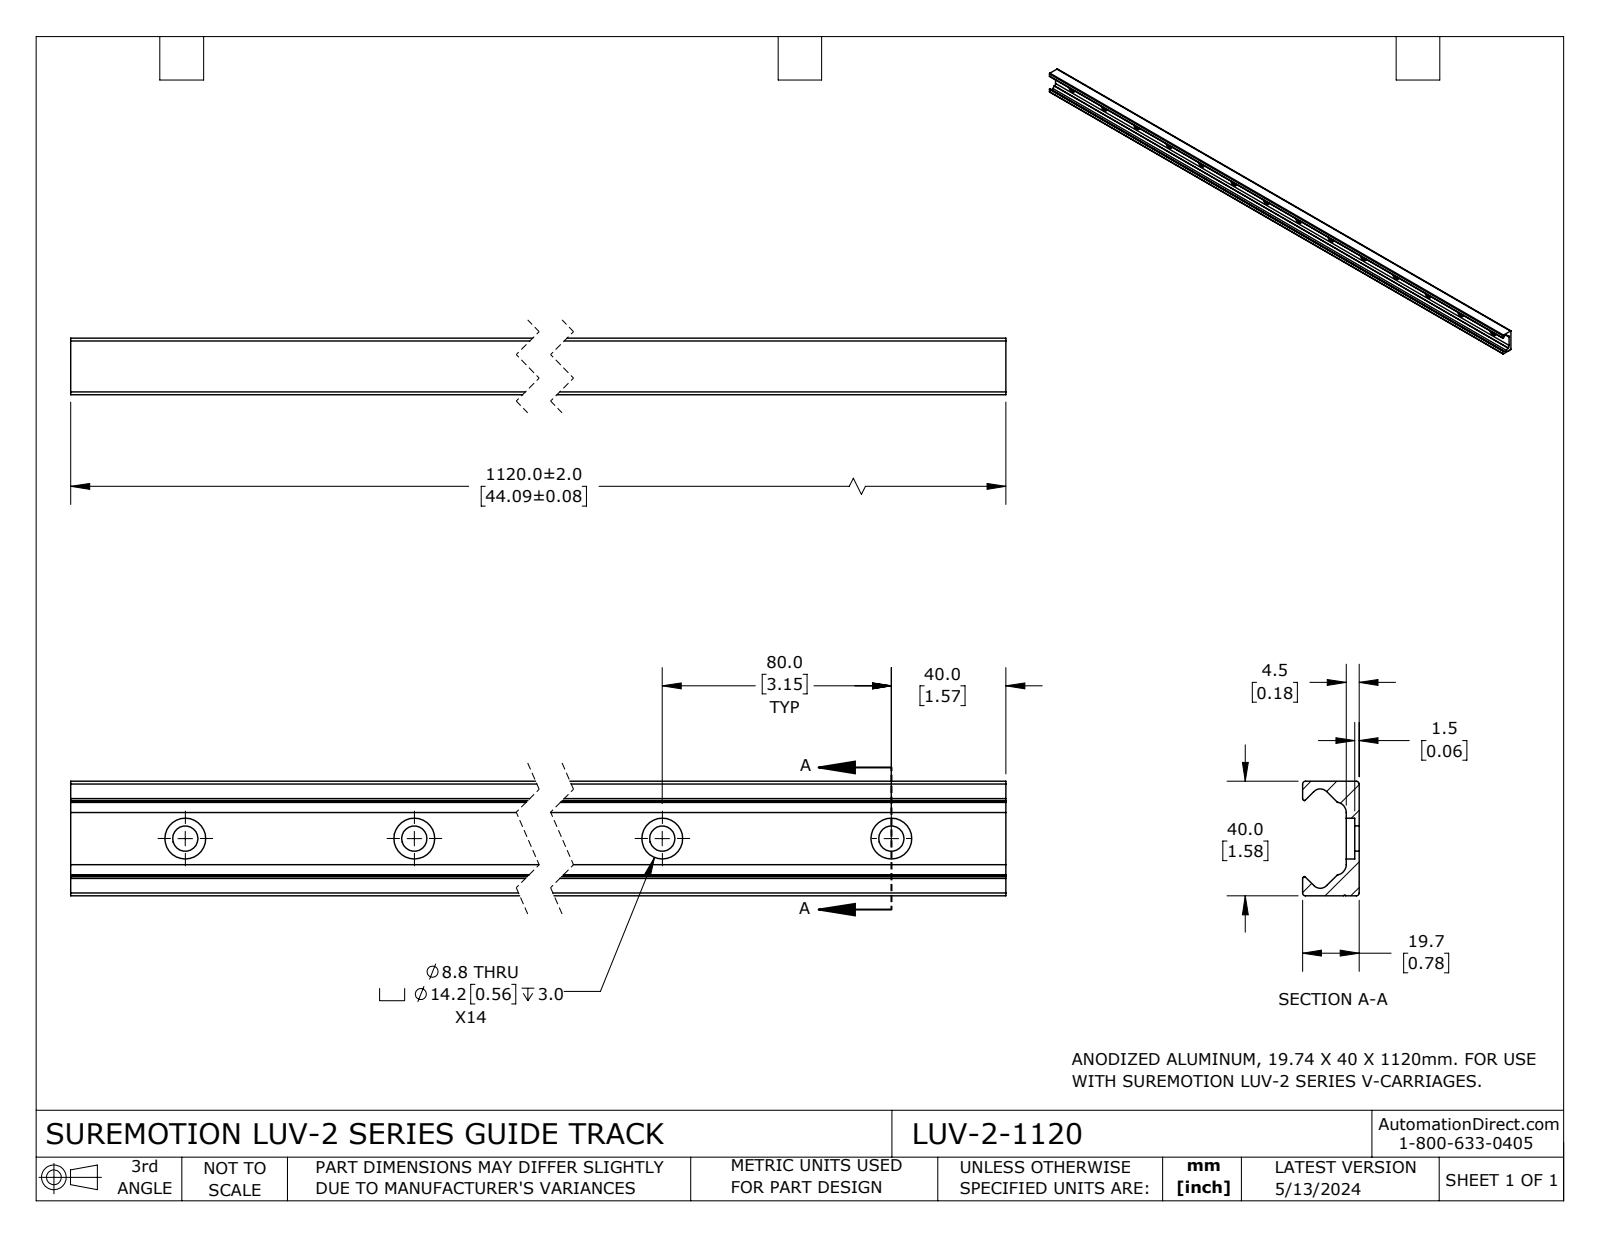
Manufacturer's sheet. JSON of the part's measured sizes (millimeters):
{"part_name": "LUV-2-1120", "step_written_by": "SolidWorks 2023 (CONFIG_CONTROL_DESIGN)", "units": "millimeters", "bodies": {"solids": 1, "faces": 98, "planar": 27, "cylindrical": 71, "other": 0}, "overall_size": [1120, 40.01, 19.74], "volume_mm3": 372691, "surface_area_mm2": 169963, "round_holes": [[8.81, 14], [14.25, 14]], "partial_cylinders_radius": [[0.99, 4], [0.43, 2], [0.64, 2], [0.64, 2], [3.18, 2], [3.61, 2], [0.33, 1]], "face_to_face_distances": [40.02, 4.5, 19.74, 15.24, 26.37, 1.5, 3, 18.24, 1120], "hole_center_spacings": [80, 160, 240, 320, 400, 480, 560, 640]}
